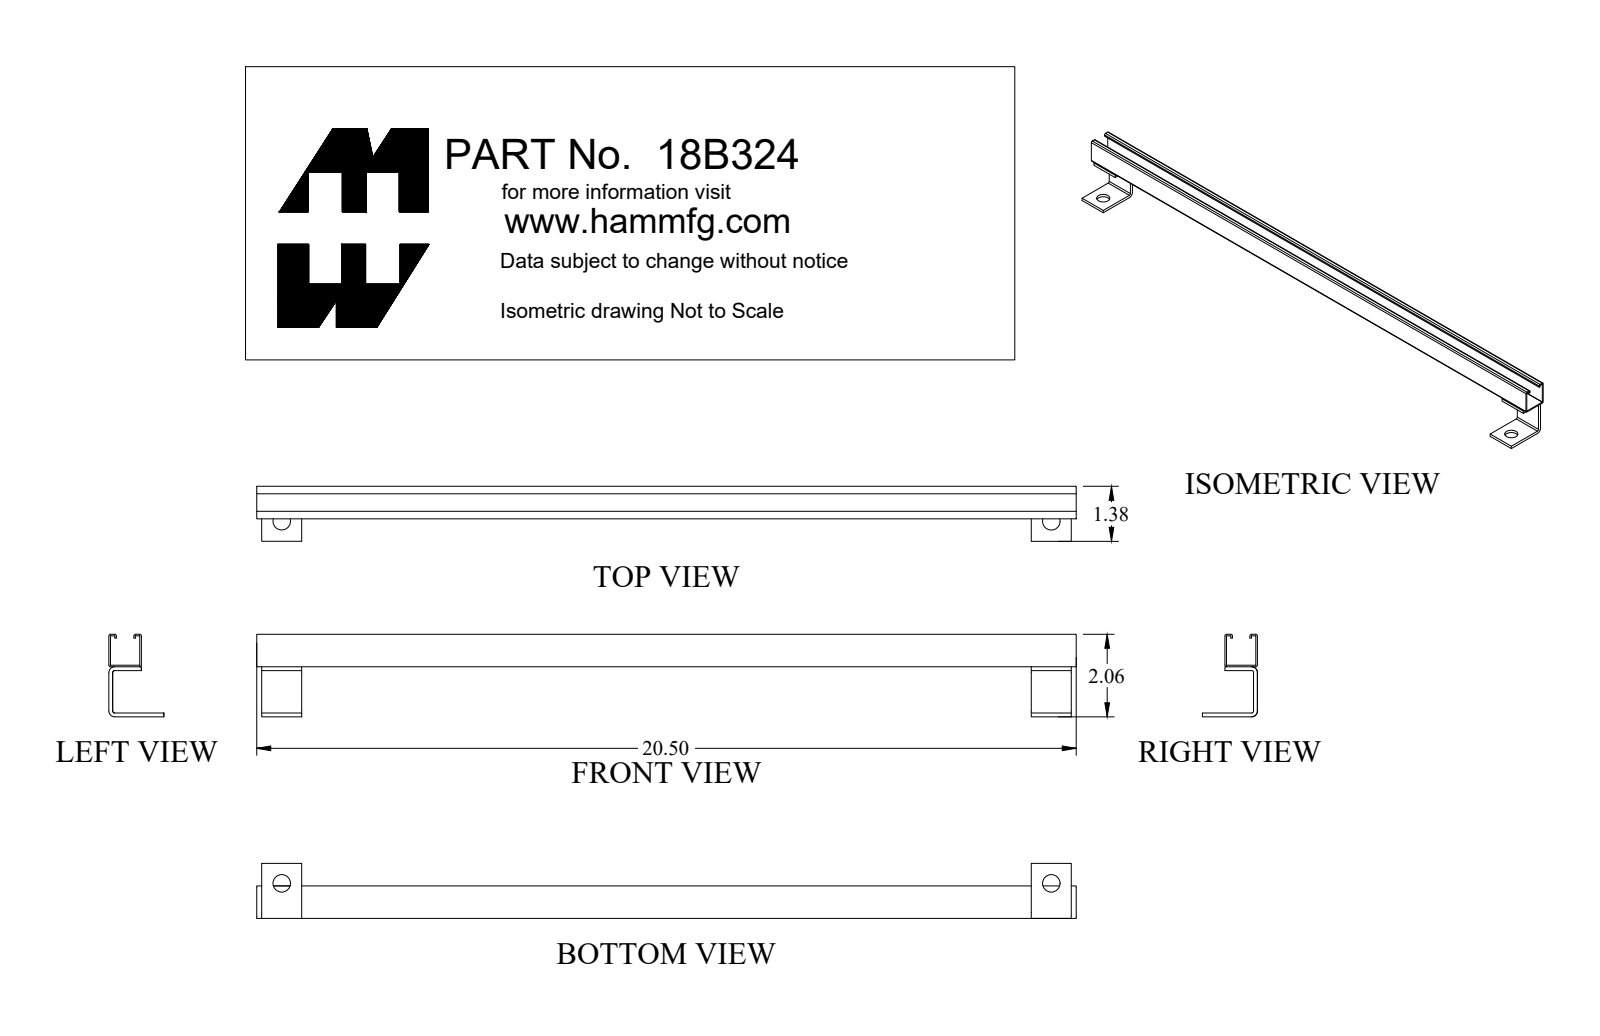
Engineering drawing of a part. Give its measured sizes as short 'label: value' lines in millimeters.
name: 18B324
written by: SolidWorks 2018 (AUTOMOTIVE_DESIGN)
unit: mm
bodies: 3 solids, 60 faces (38 planar, 22 cylindrical, 0 other)
size: 520.7 × 52.4 × 35
volume: 45 720 mm³; area: 81 680 mm²
holes: 2× ⌀11.1
rounds: 6× R1.1, 4× R1.2, 4× R3.6
face distances: 1, 19.6, 20.7, 18.6, 19.6, 2.4, 20.7, 18.6, 3.8, 15.9
hole spacings: 489
